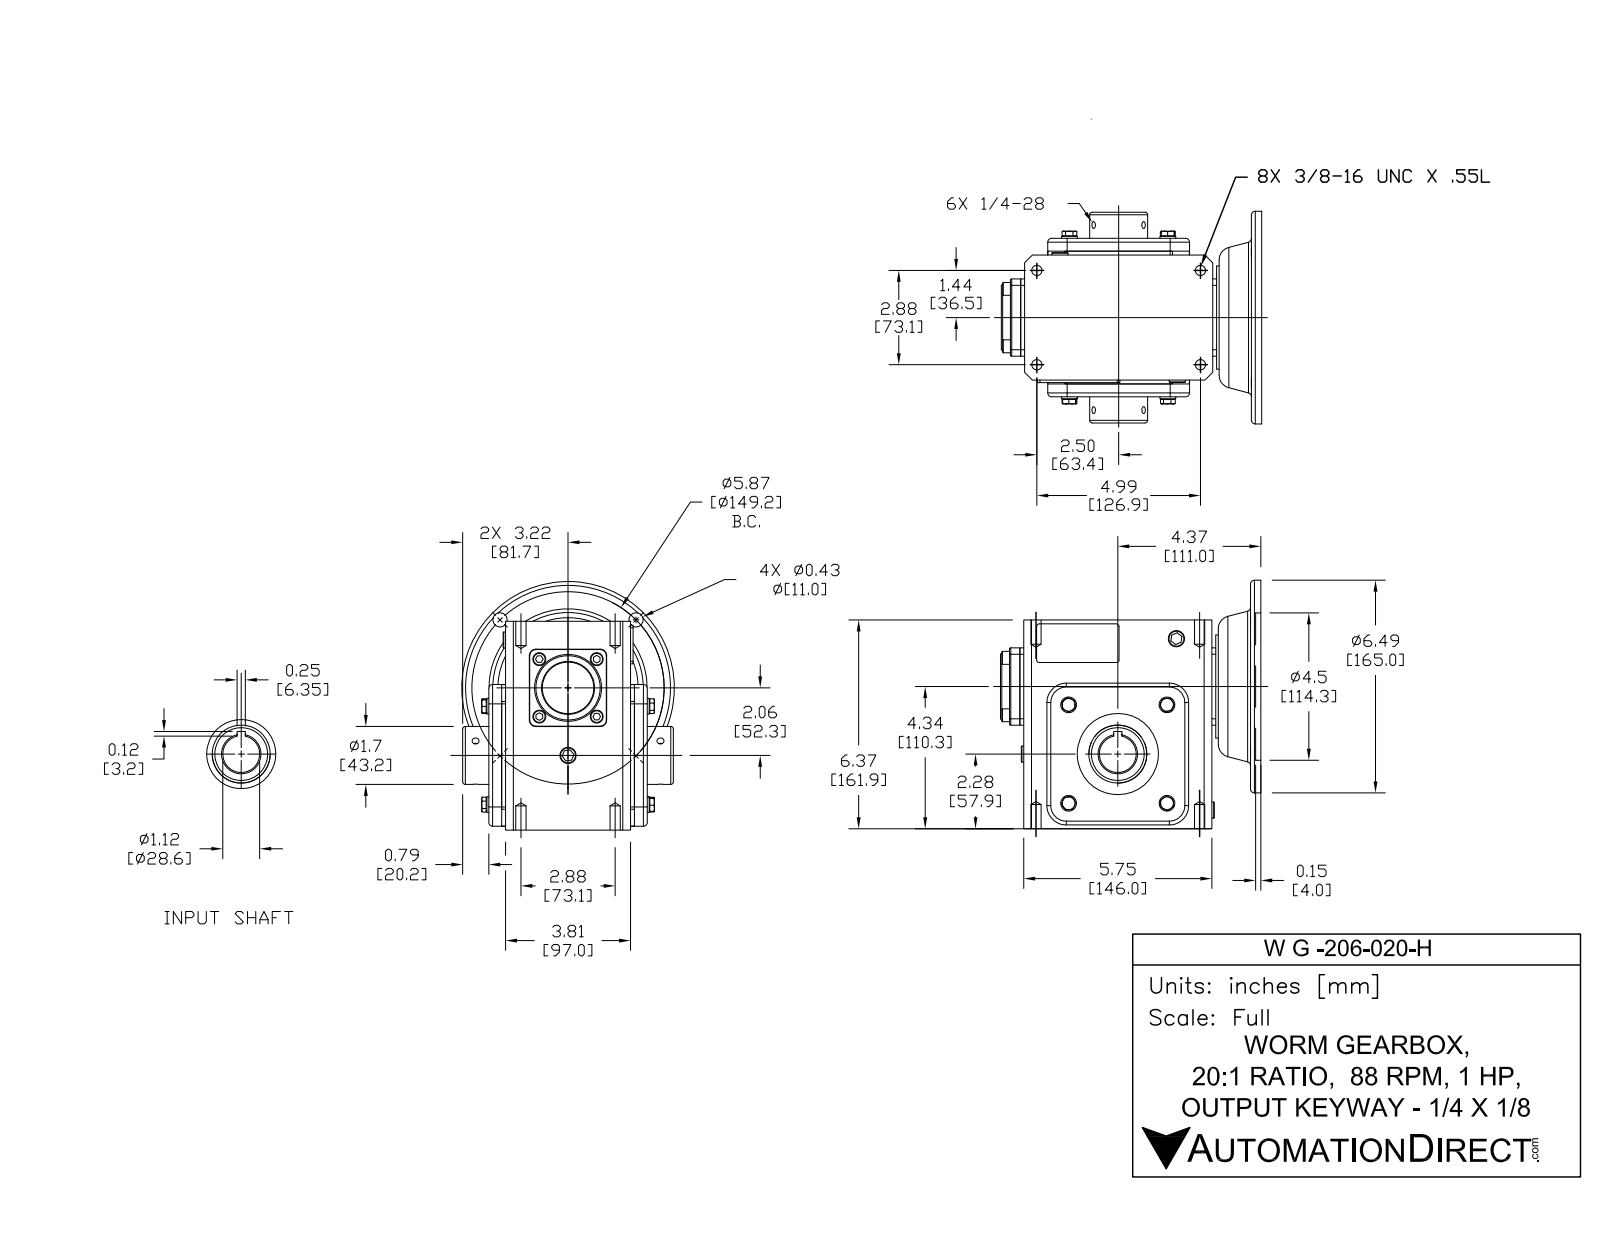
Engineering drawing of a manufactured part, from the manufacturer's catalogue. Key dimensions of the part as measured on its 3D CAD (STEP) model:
Part name (STEP PRODUCT): WG-206-020-H
STEP written by: SolidWorks 2015 (CONFIG_CONTROL_DESIGN)
Units: inches
Bodies: 45 solids, 628 faces (304 planar, 198 cylindrical, 126 other)
Overall size (bounding box): 7.953 × 7.591 × 6.496
Volume: 171 in³ · Surface area: 463.1 in²
Round holes (diameter × count): ⌀0.213 ×6, ⌀0.313 ×4, ⌀0.406 ×4, ⌀0.591 ×1, ⌀0.625 ×1, ⌀1.125 ×1, ⌀1.457 ×1, ⌀1.772 ×1, ⌀2.402 ×1, ⌀3.543 ×1, ⌀4.5 ×1
Round bosses / shafts (diameter × count): ⌀0.394 ×8, ⌀0.48 ×4, ⌀6.496 ×1, ⌀3.15 ×1, ⌀2.047 ×1, ⌀1.575 ×1, ⌀1.181 ×1, ⌀1.142 ×1
Partial cylindrical surfaces — rounded edges, fillets, slot ends (radius × count): R0.079 ×8, R0.118 ×8, R0.197 ×4, R0.591 ×4, R0.02 ×2, R0.039 ×2, R2.717 ×1
Main face-to-face distances: 0.118, 4.055, 0.394, 4.331, 3.937, 0.512, 4.449, 6.375, 5.866, 1.181
Hole centre spacings: 2.858, 2.937, 4.154, 4.943, 5.65, 2.077, 2.88, 4.631
